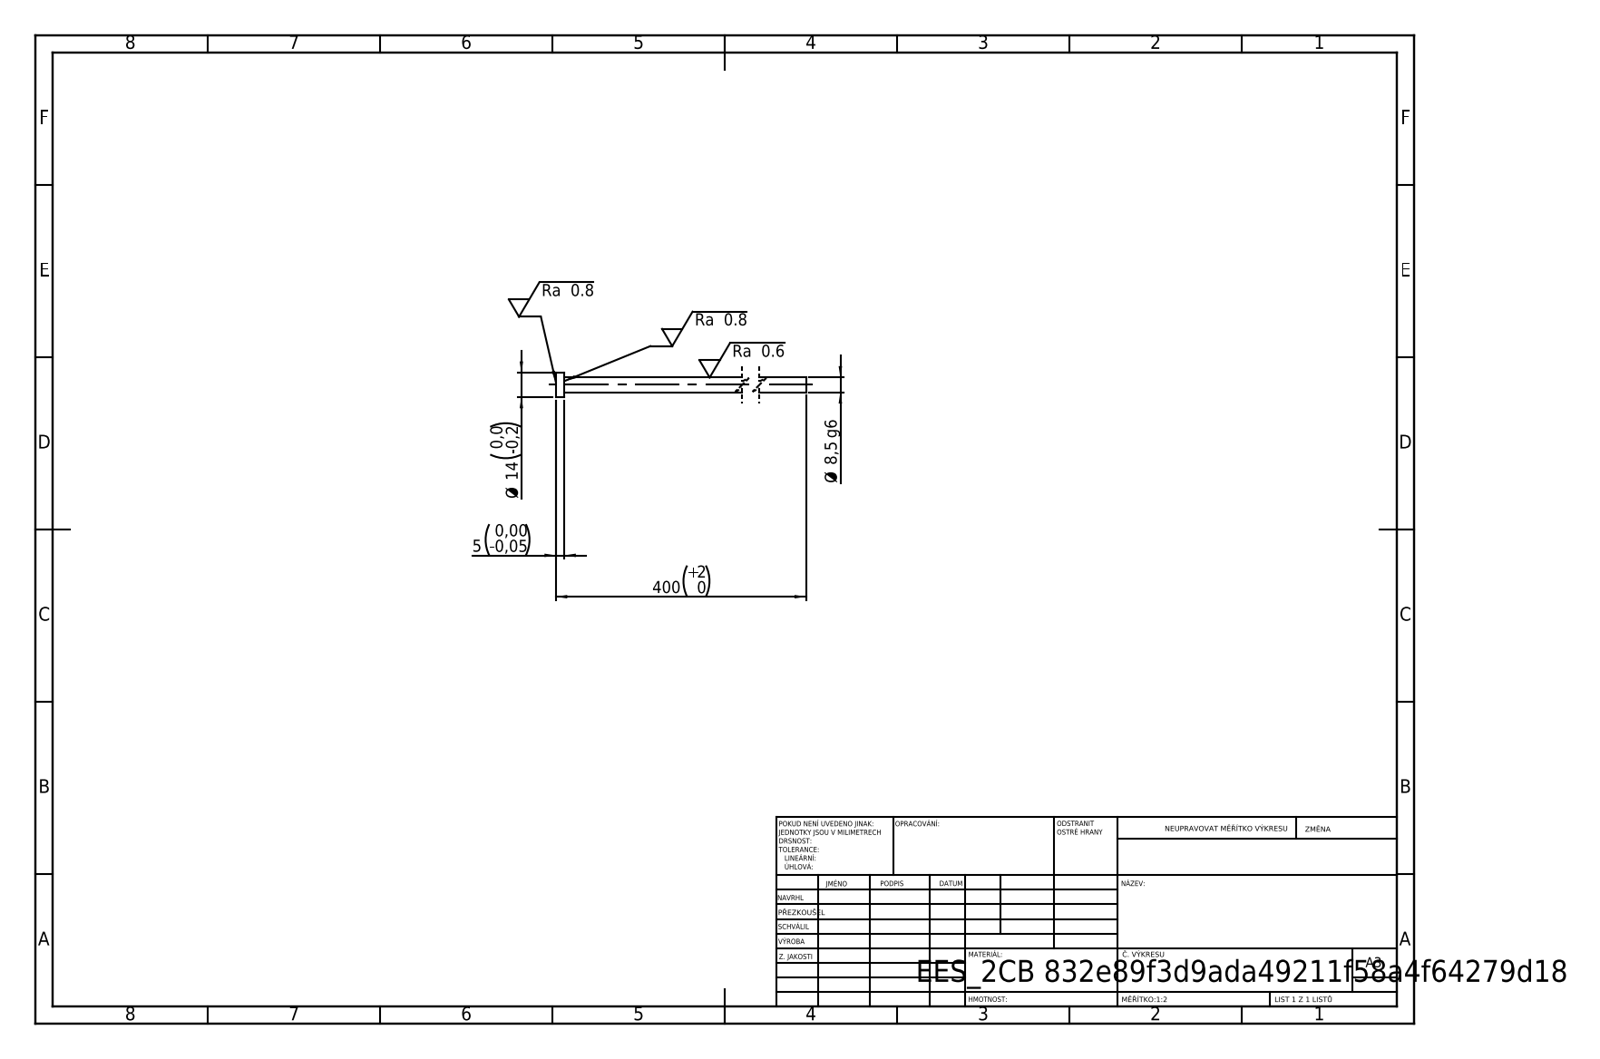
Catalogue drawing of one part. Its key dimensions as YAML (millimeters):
step_written_by: "SolidWorks 2019 (CONFIG_CONTROL_DESIGN)"
units: millimeters
bodies: {solids: 1, faces: 7, planar: 3, cylindrical: 4, other: 0}
overall_size: [400, 14, 14]
volume: 23184
surface_area: 11076
round_bosses_or_shafts:
  - {diameter: 14, count: 1}
  - {diameter: 8.5, count: 1}
face_to_face_distances: [5, 400, 395]
